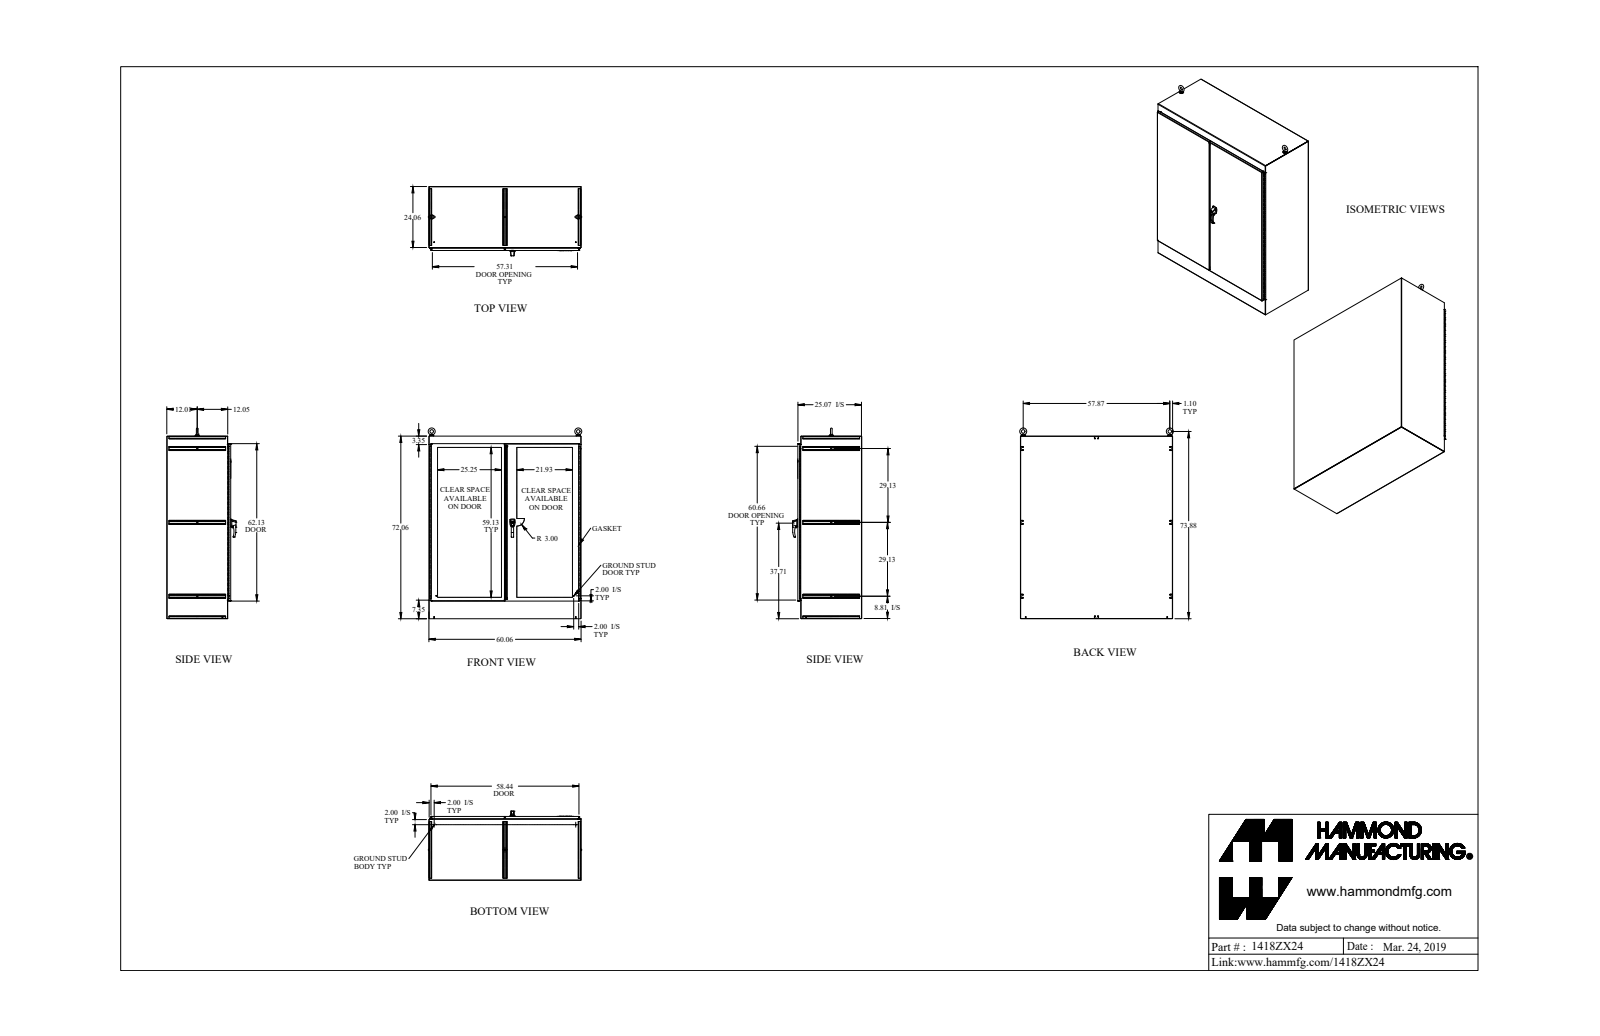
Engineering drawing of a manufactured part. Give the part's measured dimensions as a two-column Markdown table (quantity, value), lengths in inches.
| quantity | value |
| --- | --- |
| part name | 1418ZX24_Default |
| STEP written by | SolidWorks 2019 (CONFIG_CONTROL_DESIGN) |
| units | inches |
| bodies | 71 solids, 2583 faces (1198 planar, 1220 cylindrical, 165 other) |
| overall size | 75.713 × 61.119 × 27.337 |
| volume | 1 836 in³ |
| surface area | 35 782 in² |
| round holes (diameter × count) | 0.304 × 20, 0.5 × 4, 0.11 × 2, 0.25 × 2, 0.257 × 2, 0.28 × 2, 0.281 × 2, 0.313 × 2, 0.39 × 2, 0.413 × 2, 0.527 × 2, 0.625 × 2 |
| round bosses / shafts (diameter × count) | 0.281 × 6, 0.25 × 4, 1.75 × 2, 1.5 × 2, 1.25 × 2, 1 × 2, 0.75 × 2, 0.738 × 2 |
| partial cylindrical surfaces (radius × count) | 0.043 × 54, 0.138 × 48, 0.125 × 22, 0.048 × 20, 0.143 × 20, 0.018 × 16, 0.06 × 10, 0.05 × 8 |
| main face-to-face distances | 0.095, 0.125, 25.002, 25.127, 25.097, 25.222, 59.965, 71.965, 59.87, 60.06 |
| hole center spacings | 6, 58.636, 12, 59.55, 18, 61.043, 24, 63.073 |
